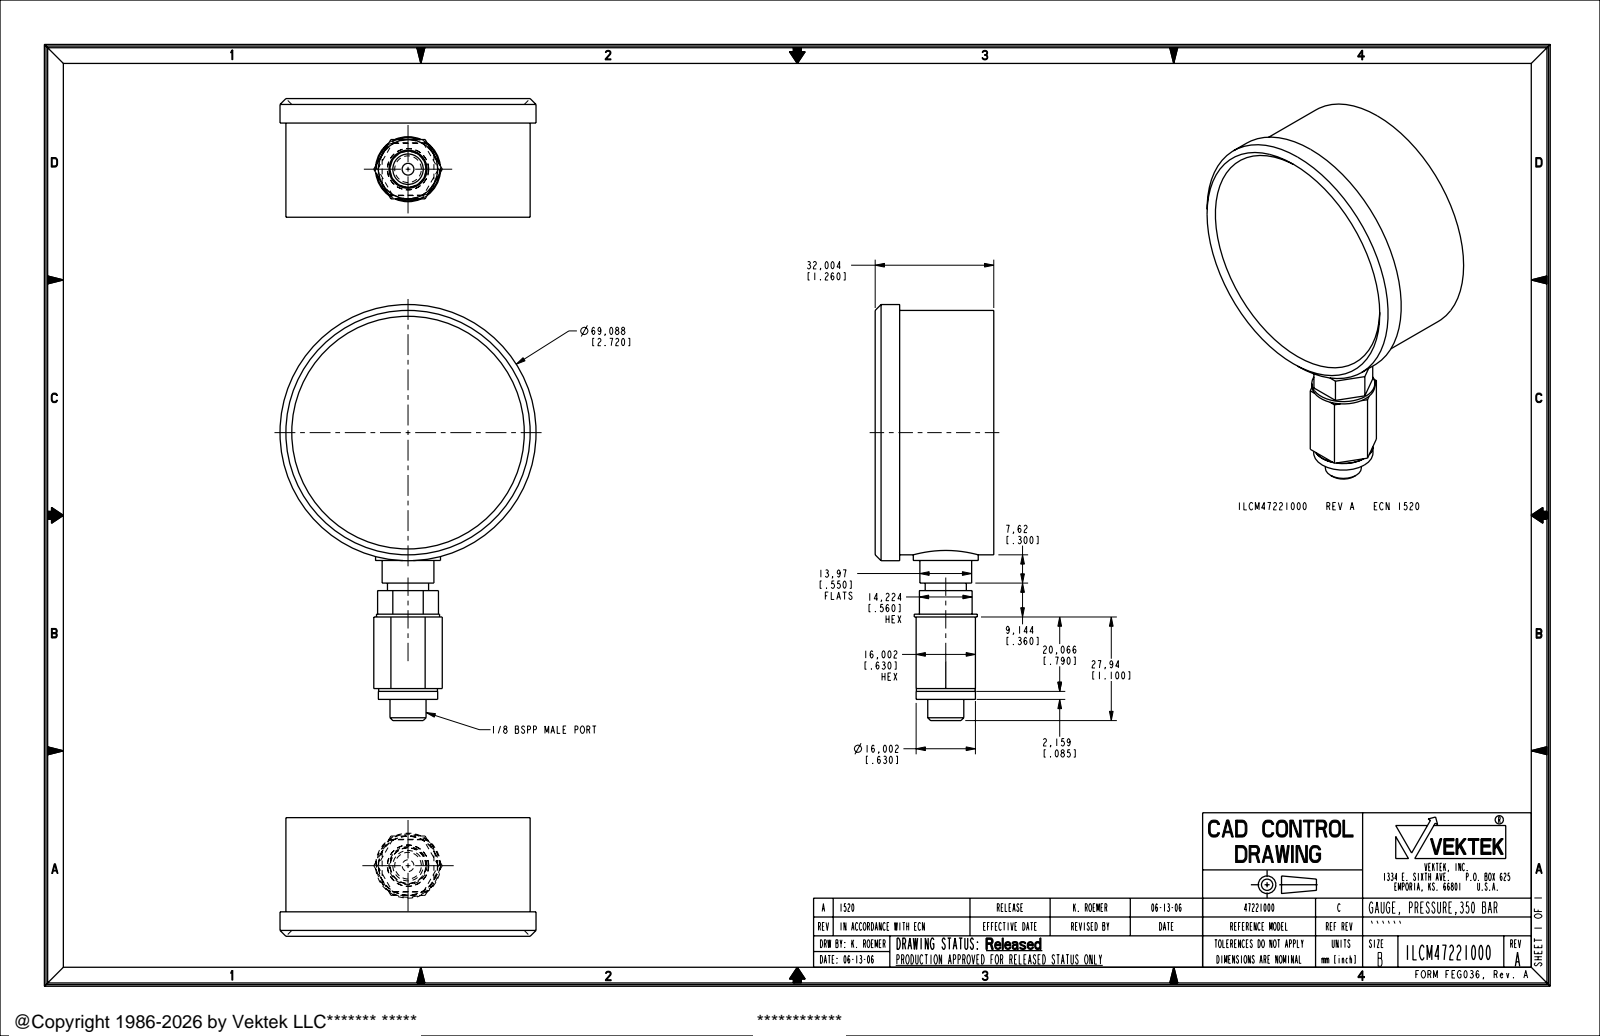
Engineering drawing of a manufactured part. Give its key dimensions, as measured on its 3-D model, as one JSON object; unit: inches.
{"part_name": "ILCM47221000", "step_written_by": "PRO/ENGINEER BY PARAMETRIC TECHNOLOGY CORPORATION, 2004290 (AUTOMOTIVE_DESIGN_CC2)", "units": "inches", "bodies": {"solids": 1, "faces": 80, "planar": 44, "cylindrical": 28, "other": 8}, "overall_size": [4.417, 2.72, 1.26], "volume_in3": 6.952, "surface_area_in2": 26.87, "round_holes": [[0.125, 1], [0.404, 1], [0.44, 1]], "round_bosses_or_shafts": [[2.72, 1], [2.595, 1], [0.69, 1], [0.67, 1], [0.63, 1], [0.625, 1], [0.437, 1], [0.383, 1]], "partial_cylinders_radius": [[0.12, 4]], "face_to_face_distances": [1.197, 0.63, 0.035, 1, 0.197, 0.595, 0.195, 0.825, 0.805, 1.002]}
